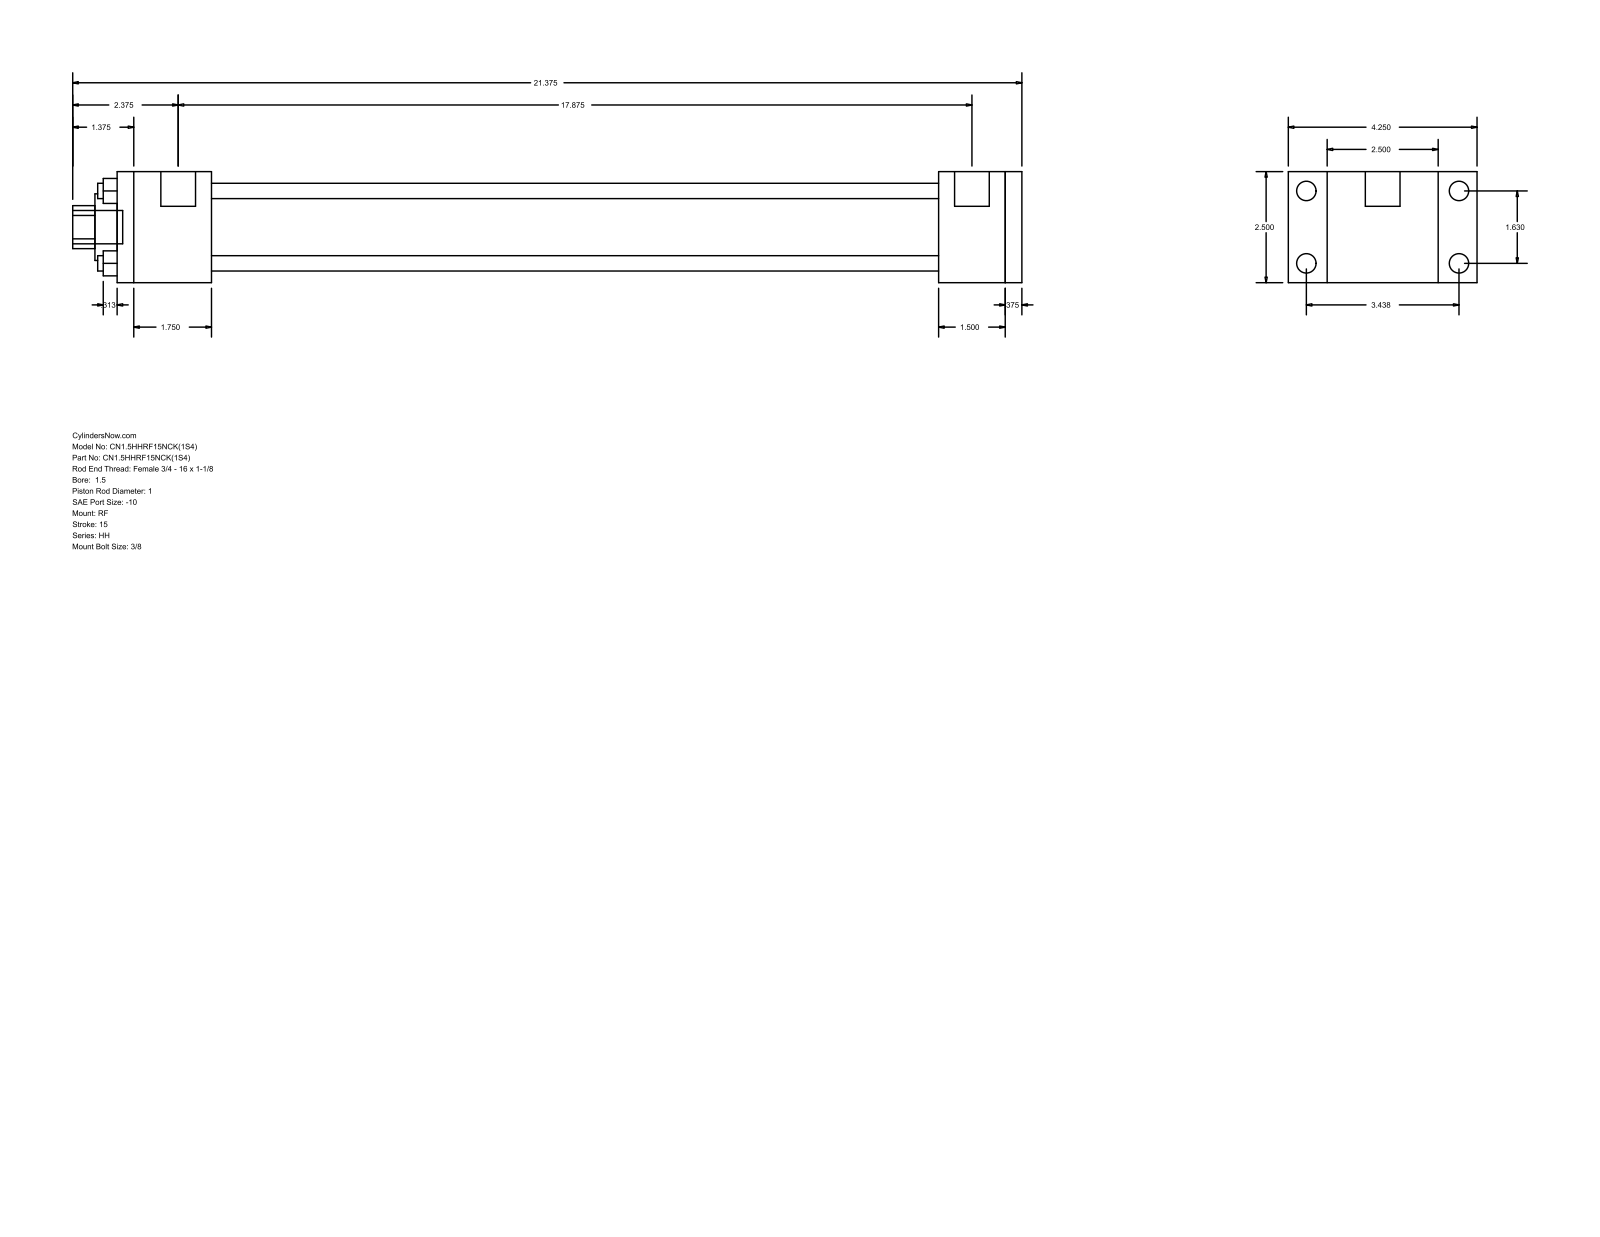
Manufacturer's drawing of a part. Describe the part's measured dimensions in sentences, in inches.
The part is named "HH_RF__0150_1". Its 3-D file was written by "GSSL Pune (CONFIG_CONTROL_DESIGN)". It is 0 solids with 92 faces: 64 planar, 28 cylindrical and 0 other. Overall it measures 21.375 by 4.25 by 2.5 inches. Round holes: 4 of diameter 0.345, 1 of diameter 1, 1 of diameter 1.5, 1 of diameter 1.75. Round bosses or shafts: 4 of diameter 0.438, 4 of diameter 0.219, 2 of diameter 0.781, 1 of diameter 0.75. Partial cylindrical surfaces (rounded edges, fillets, slot ends): 1 of radius 0.484. The main face-to-face distances are 2.5, 0.375, 16.375, 17.875, 18.25, 1.5, 1.875, 2.125, 18.5, 20. The hole center spacings are 1.152, 1.63, 2.305.
